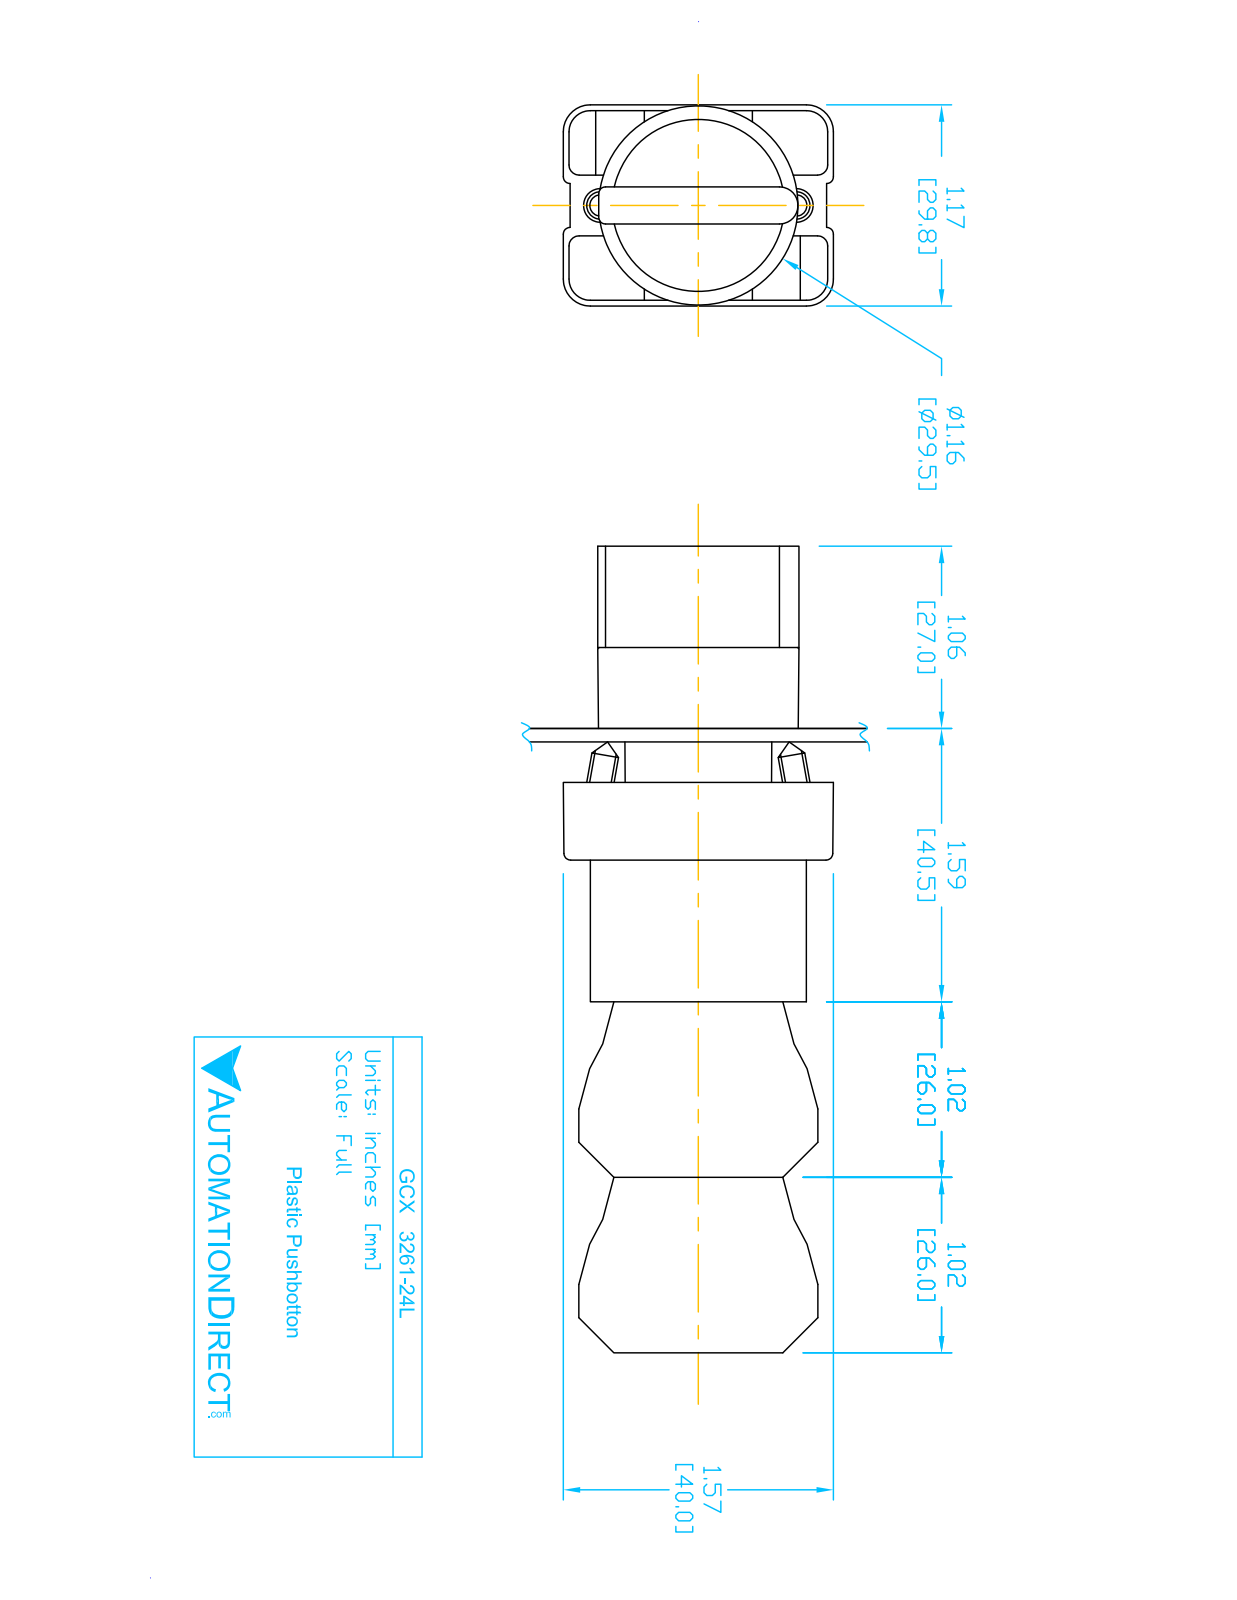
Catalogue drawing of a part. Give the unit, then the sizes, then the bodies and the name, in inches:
Units: inches
Overall size (bounding box): 4.677 × 1.581 × 1.177
Round holes (diameter × count): ⌀0.079 ×4, ⌀0.087 ×2, ⌀0.124 ×2, ⌀0.13 ×2, ⌀0.197 ×1, ⌀0.469 ×1, ⌀0.878 ×1, ⌀0.888 ×1, ⌀1.024 ×1
Round bosses / shafts (diameter × count): ⌀0.157 ×4, ⌀1.175 ×1, ⌀1.004 ×1, ⌀0.945 ×1, ⌀0.856 ×1, ⌀0.78 ×1, ⌀0.504 ×1
Partial cylindrical surfaces — rounded edges, fillets, slot ends (radius × count): R0.059 ×24, R0.041 ×12, R0.124 ×12, R0.157 ×12, R0.039 ×9, R0.02 ×2, R0.063 ×2, R0.079 ×2
Main face-to-face distances: 0.579, 0.593, 1.024, 1.171, 0.014, 0.827, 1.85, 3.043, 2.02, 1.193
Hole centre spacings: 0.236, 1.003, 0.974, 0.472, 0.539, 0.544, 1.083, 0.484
Volume: 4.751 in³ · Surface area: 59.22 in²
Bodies: 11 solids, 724 faces (488 planar, 193 cylindrical, 43 other)
Part name (STEP PRODUCT): ECX1050; GCX3261L OPERATOR; ecx1040; ecx1030 (+2 more)
STEP written by: SolidWorks 2016 (AUTOMOTIVE_DESIGN)
